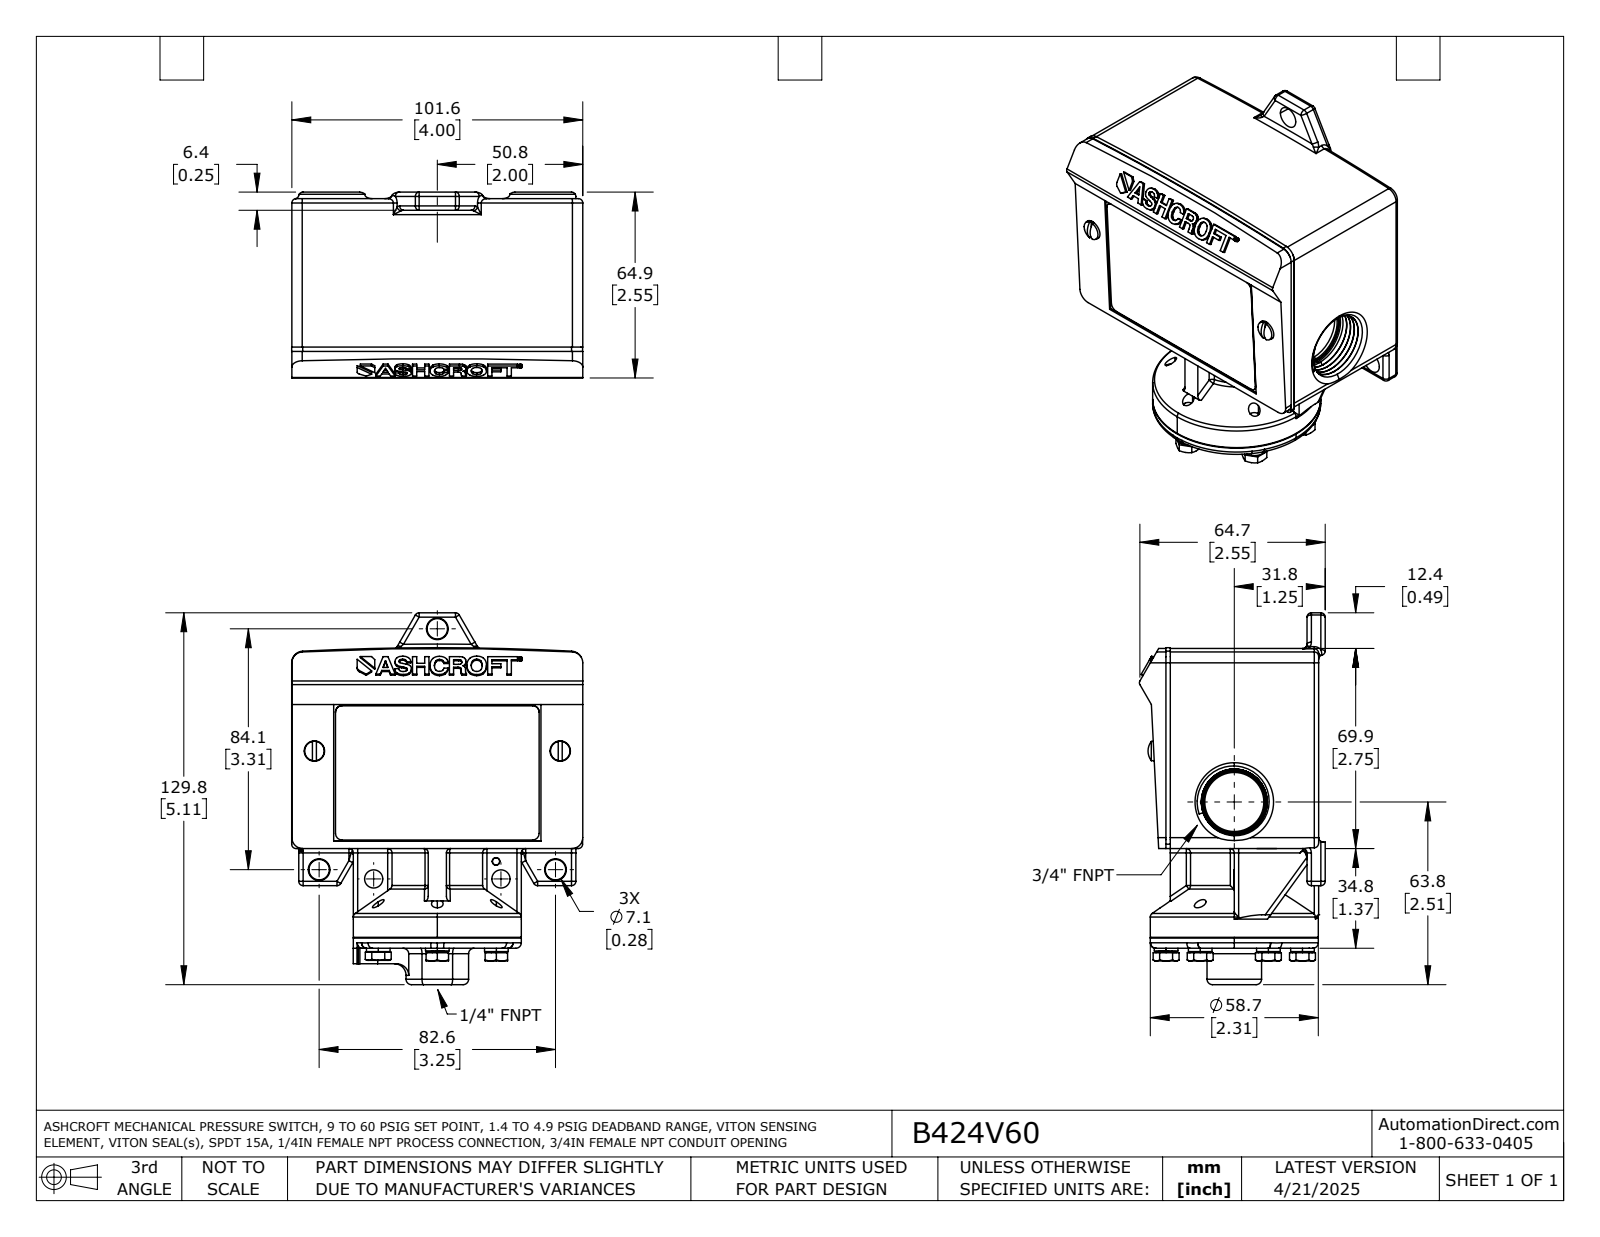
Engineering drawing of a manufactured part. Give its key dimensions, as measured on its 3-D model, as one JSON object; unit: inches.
{"part_name": "B424V60", "step_written_by": "SolidWorks 2021 (AUTOMOTIVE_DESIGN)", "units": "inches", "bodies": {"solids": 2, "faces": 1259, "planar": 345, "cylindrical": 472, "other": 442}, "overall_size": [5.111, 4.003, 2.555], "volume_in3": 28.57, "surface_area_in2": 84.51, "round_holes": [[0.161, 6], [0.192, 5], [0.209, 5], [0.187, 4], [0.28, 2], [0.455, 1], [0.812, 1]], "round_bosses_or_shafts": [[0.325, 6], [0.278, 6], [0.19, 5], [0.27, 2], [0.25, 2], [2.31, 1]], "partial_cylinders_radius": [[0.06, 92], [0.03, 5], [0.075, 4], [0.09, 4], [0.15, 4], [0.01, 2], [0.094, 2], [0.16, 2]], "face_to_face_distances": [4, 0.015, 1.37, 0.09, 3.91, 0.44, 3.56, 3.47, 0.35, 0.845], "hole_center_spacings": [0.937, 1.624, 1.875, 0.938, 3.38]}
